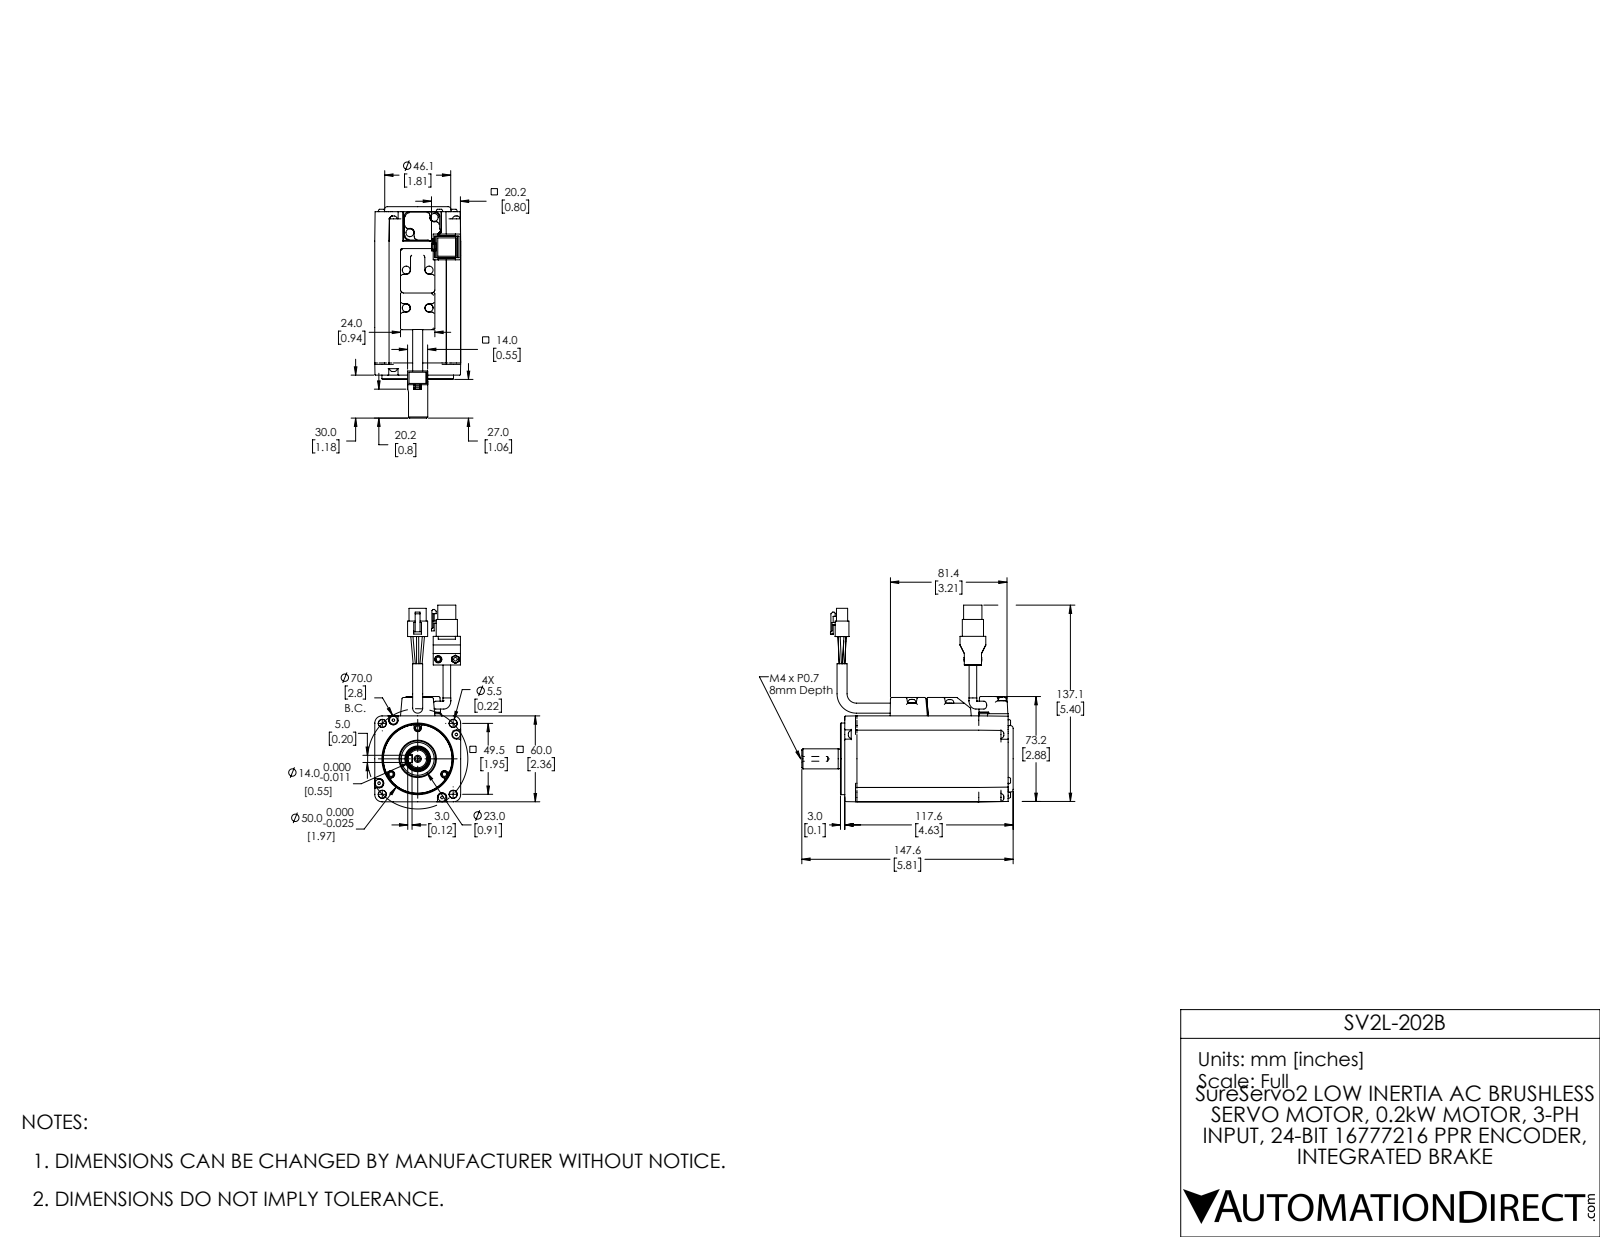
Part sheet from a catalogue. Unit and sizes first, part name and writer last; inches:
Units: inches
Overall size (bounding box): 5.811 × 5.407 × 2.363
Round holes (diameter × count): ⌀0.201 ×2, ⌀0.13 ×1, ⌀0.906 ×1, ⌀1.89 ×1
Round bosses / shafts (diameter × count): ⌀0.217 ×8, ⌀0.059 ×6, ⌀0.276 ×2, ⌀0.181 ×2, ⌀0.142 ×2, ⌀0.098 ×2, ⌀1.969 ×1, ⌀1.831 ×1
Partial cylindrical surfaces — rounded edges, fillets, slot ends (radius × count): R0.039 ×52, R0.02 ×28, R0.079 ×28, R0.118 ×16, R0.03 ×5, R0.085 ×3, R0.1 ×3, R0.11 ×3
Main face-to-face distances: 2.362, 0.394, 1.969, 2.363, 0.118, 1.575, 0.138, 4.748, 4.61, 4.63
Hole centre spacings: 0.472, 2.794, 2.927
Volume: 25.4 in³ · Surface area: 73.69 in²
Bodies: 1 solid, 775 faces (315 planar, 244 cylindrical, 216 other)
Part name (STEP PRODUCT): ECM-A3H-CX0602SSX 202B r1 ext coord. C2 r1b
STEP written by: SolidWorks 2017 (AUTOMOTIVE_DESIGN)
